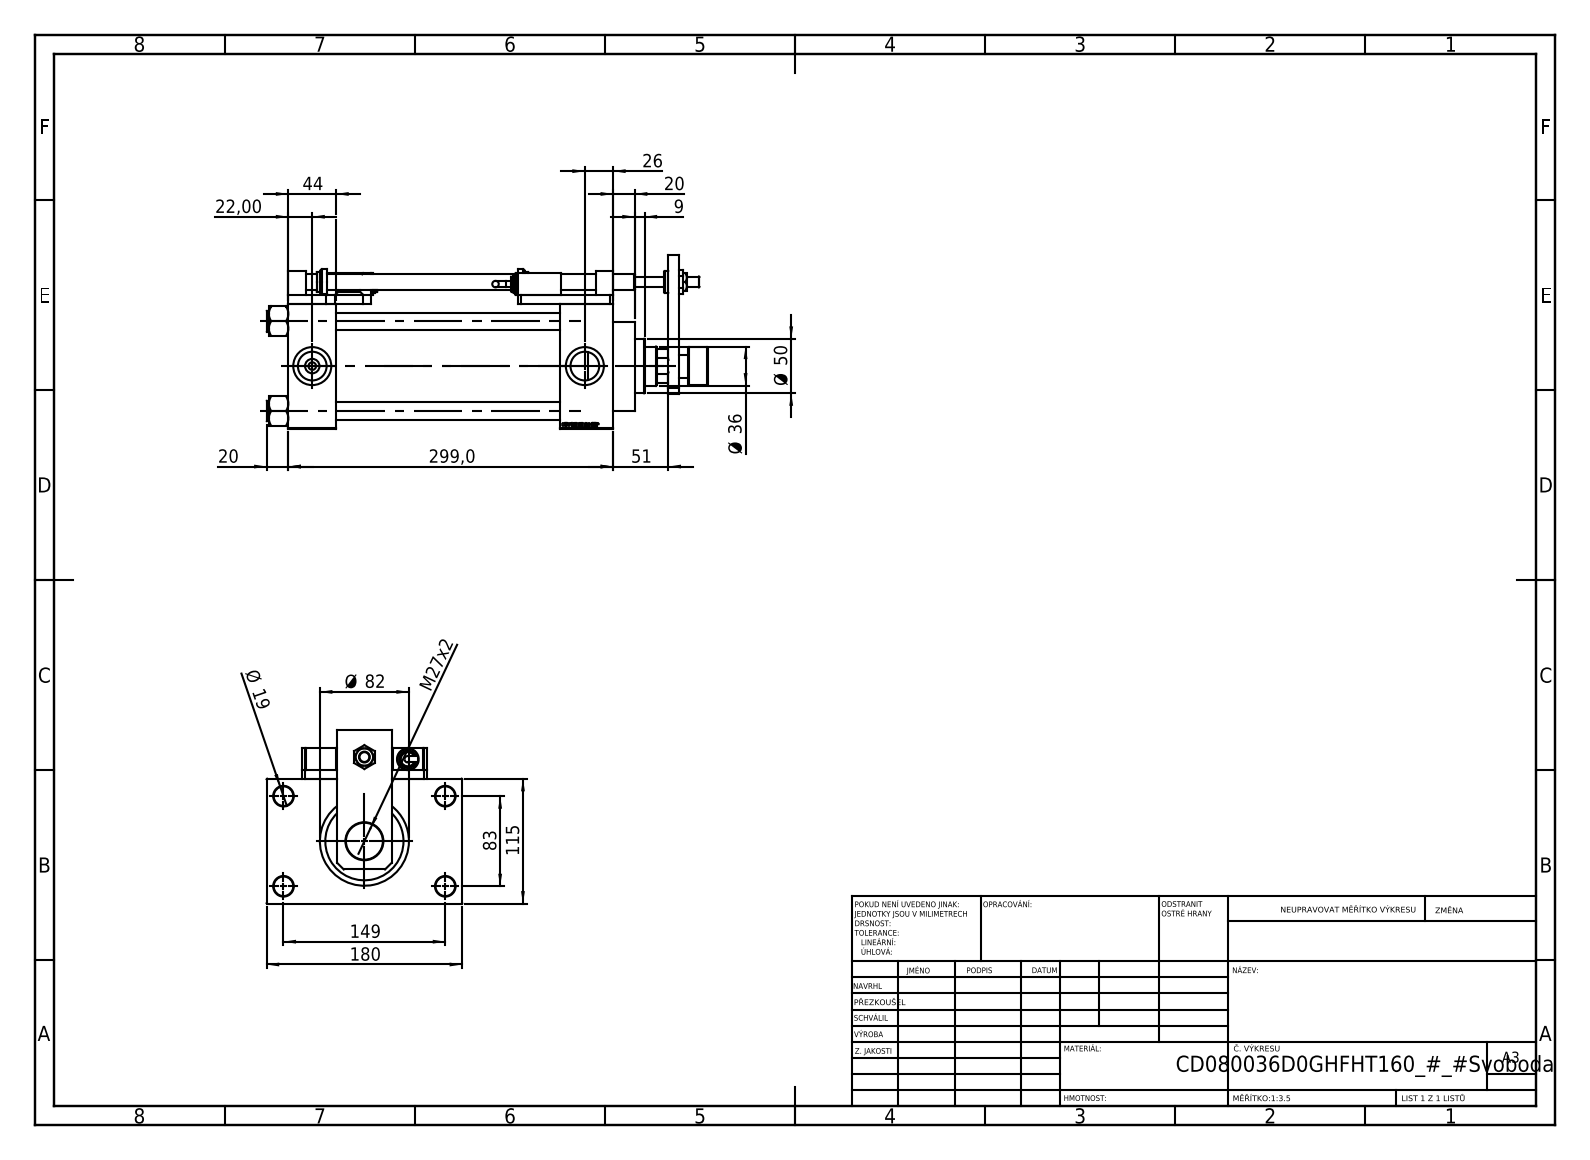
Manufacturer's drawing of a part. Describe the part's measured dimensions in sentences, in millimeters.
The part is named "V215CD_VC_A; V215CD_SWITCH_Q_TYC; V215CD_SWITCH_Q_BLOK; V215CD_SWITCH_Q_MAGNET (+7 more)". Its 3-D file was written by "SolidWorks 2019 (CONFIG_CONTROL_DESIGN)". It is 25 solids with 1393 faces: 670 planar, 160 cylindrical and 563 other. Overall it measures 406 by 180 by 160 millimeters. Its volume is 2 683 000 cubic millimeters and its surface area 516 539 square millimeters. Round holes: 4 of diameter 8.5, 4 of diameter 13.5, 4 of diameter 16, 4 of diameter 18, 2 of diameter 7, 2 of diameter 26.44, 2 of diameter 35, 1 of diameter 10, 1 of diameter 14, 1 of diameter 25.5, 1 of diameter 27, 1 of diameter 36. Round bosses or shafts: 4 of diameter 19, 3 of diameter 20, 2 of diameter 16, 2 of diameter 14, 2 of diameter 6, 1 of diameter 86, 1 of diameter 82, 1 of diameter 50. Partial cylindrical surfaces (rounded edges, fillets, slot ends): 4 of radius 7.5. The main face-to-face distances are 115, 8, 49, 255, 44, 299, 250, 206, 123, 32.5. The hole center spacings are 33.15, 58.48, 82.7, 85.28, 89.24, 115.85, 142.43, 32.
